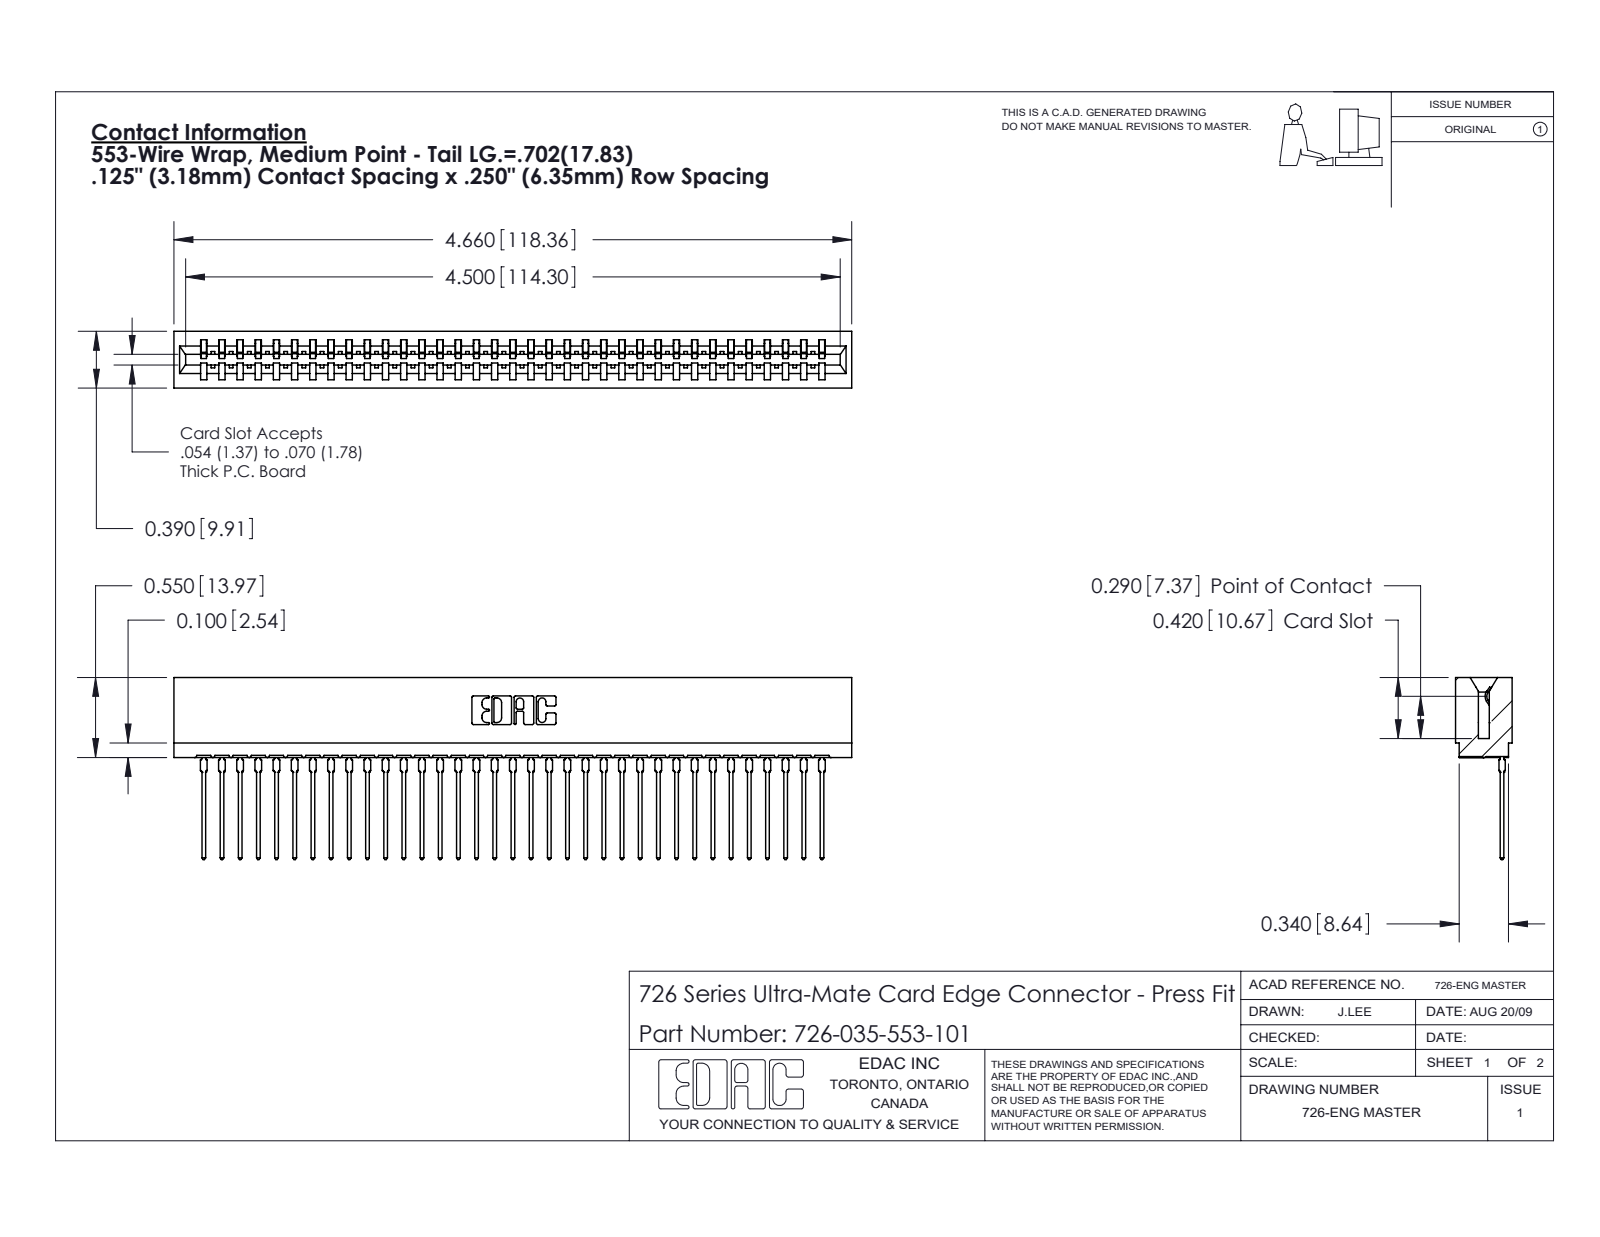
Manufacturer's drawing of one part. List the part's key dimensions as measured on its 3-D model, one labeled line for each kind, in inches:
Part name (STEP PRODUCT): 726 Part_.515 Slot Depth - 01; 746-292-001_553; 726-035-553-101
STEP written by: SolidWorks 2020 (CONFIG_CONTROL_DESIGN)
Units: inches
Bodies: 36 solids, 3877 faces (2260 planar, 707 cylindrical, 910 other)
Overall size (bounding box): 4.66 × 1.251 × 0.39
Volume: 0.656 in³ · Surface area: 26.25 in²
Partial cylindrical surfaces — rounded edges, fillets, slot ends (radius × count): R0.021 ×70, R0.015 ×36, R0.01 ×22, R0.007 ×6, R0.031 ×6, R0.005 ×4, R0.011 ×4, R0.026 ×3
Main face-to-face distances: 0.057, 0.333, 0.39, 0.25, 0.025, 0.307, 0.083, 0.5, 0.275, 0.365
